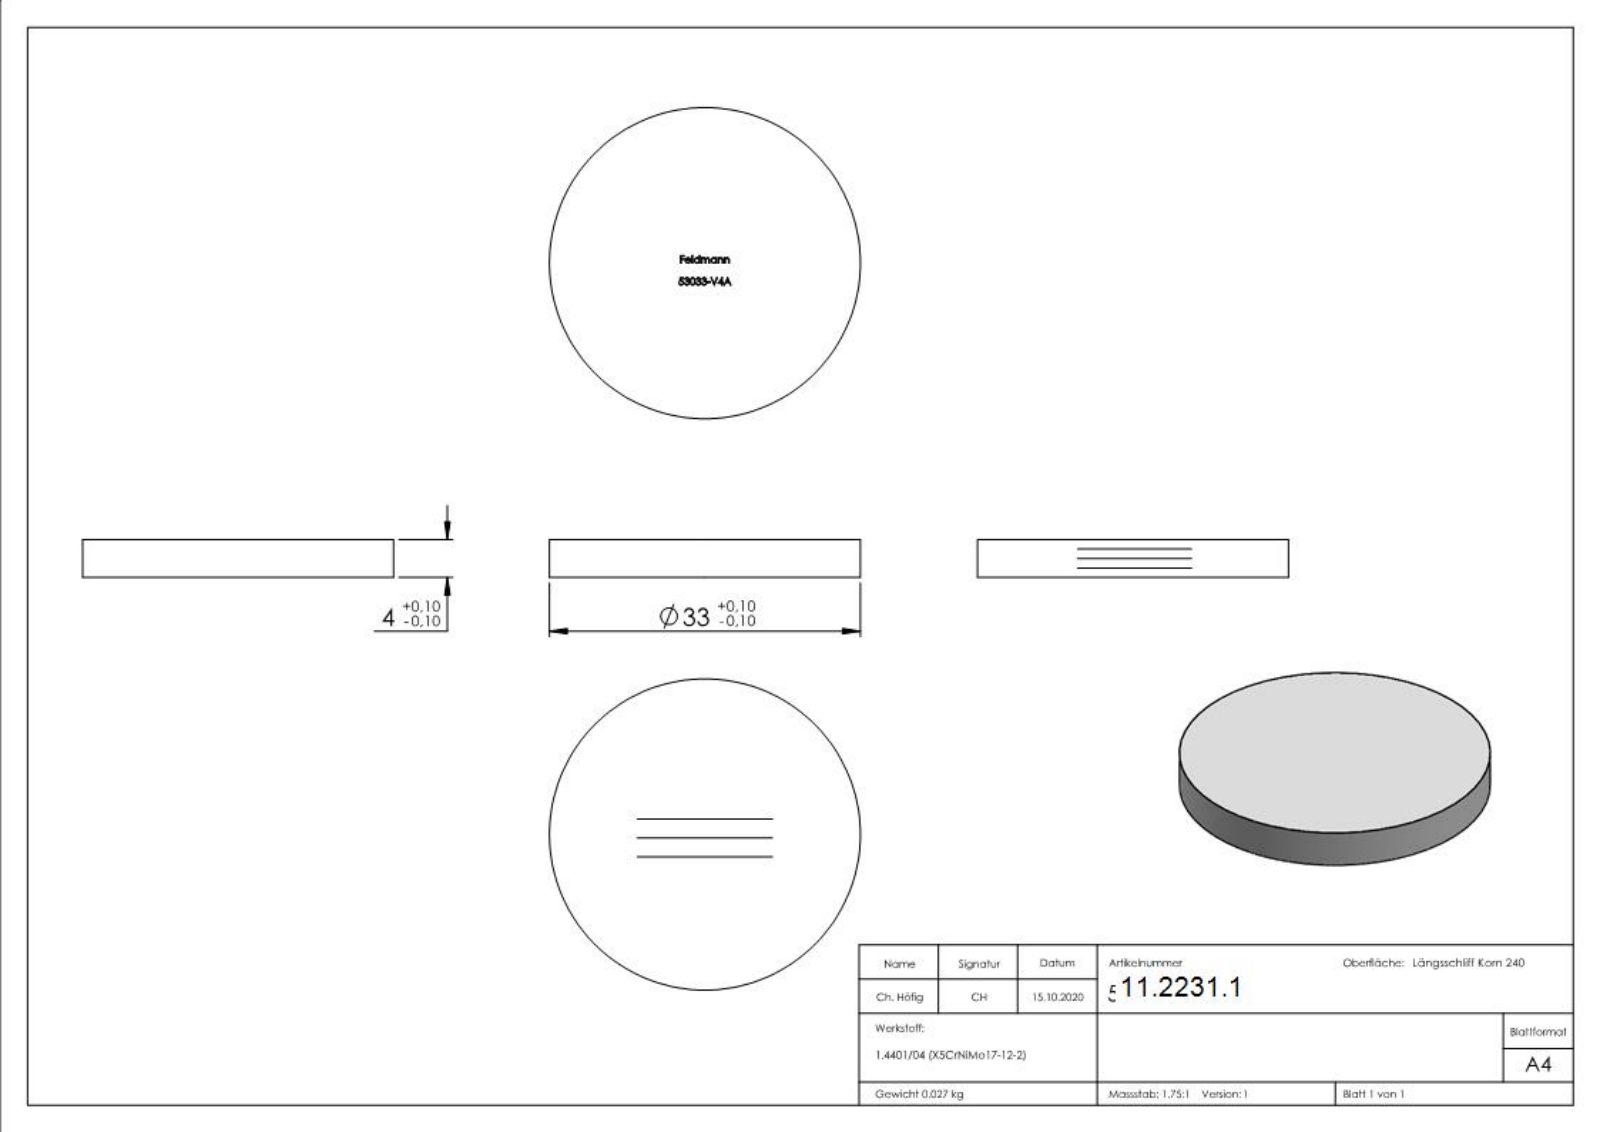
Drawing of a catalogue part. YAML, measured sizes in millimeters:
part_name: "53033-V4A"
step_written_by: "SolidWorks 2018 (CONFIG_CONTROL_DESIGN)"
units: millimeters
bodies: {solids: 1, faces: 238, planar: 129, cylindrical: 2, other: 107}
overall_size: [33, 33, 4]
volume: 3421
surface_area: 2131
round_bosses_or_shafts:
  - {diameter: 33, count: 1}
face_to_face_distances: [4, 3.9, 1.78, 0.44, 2.45, 0.83, 2.38, 0.99, 2.77, 0.67]
